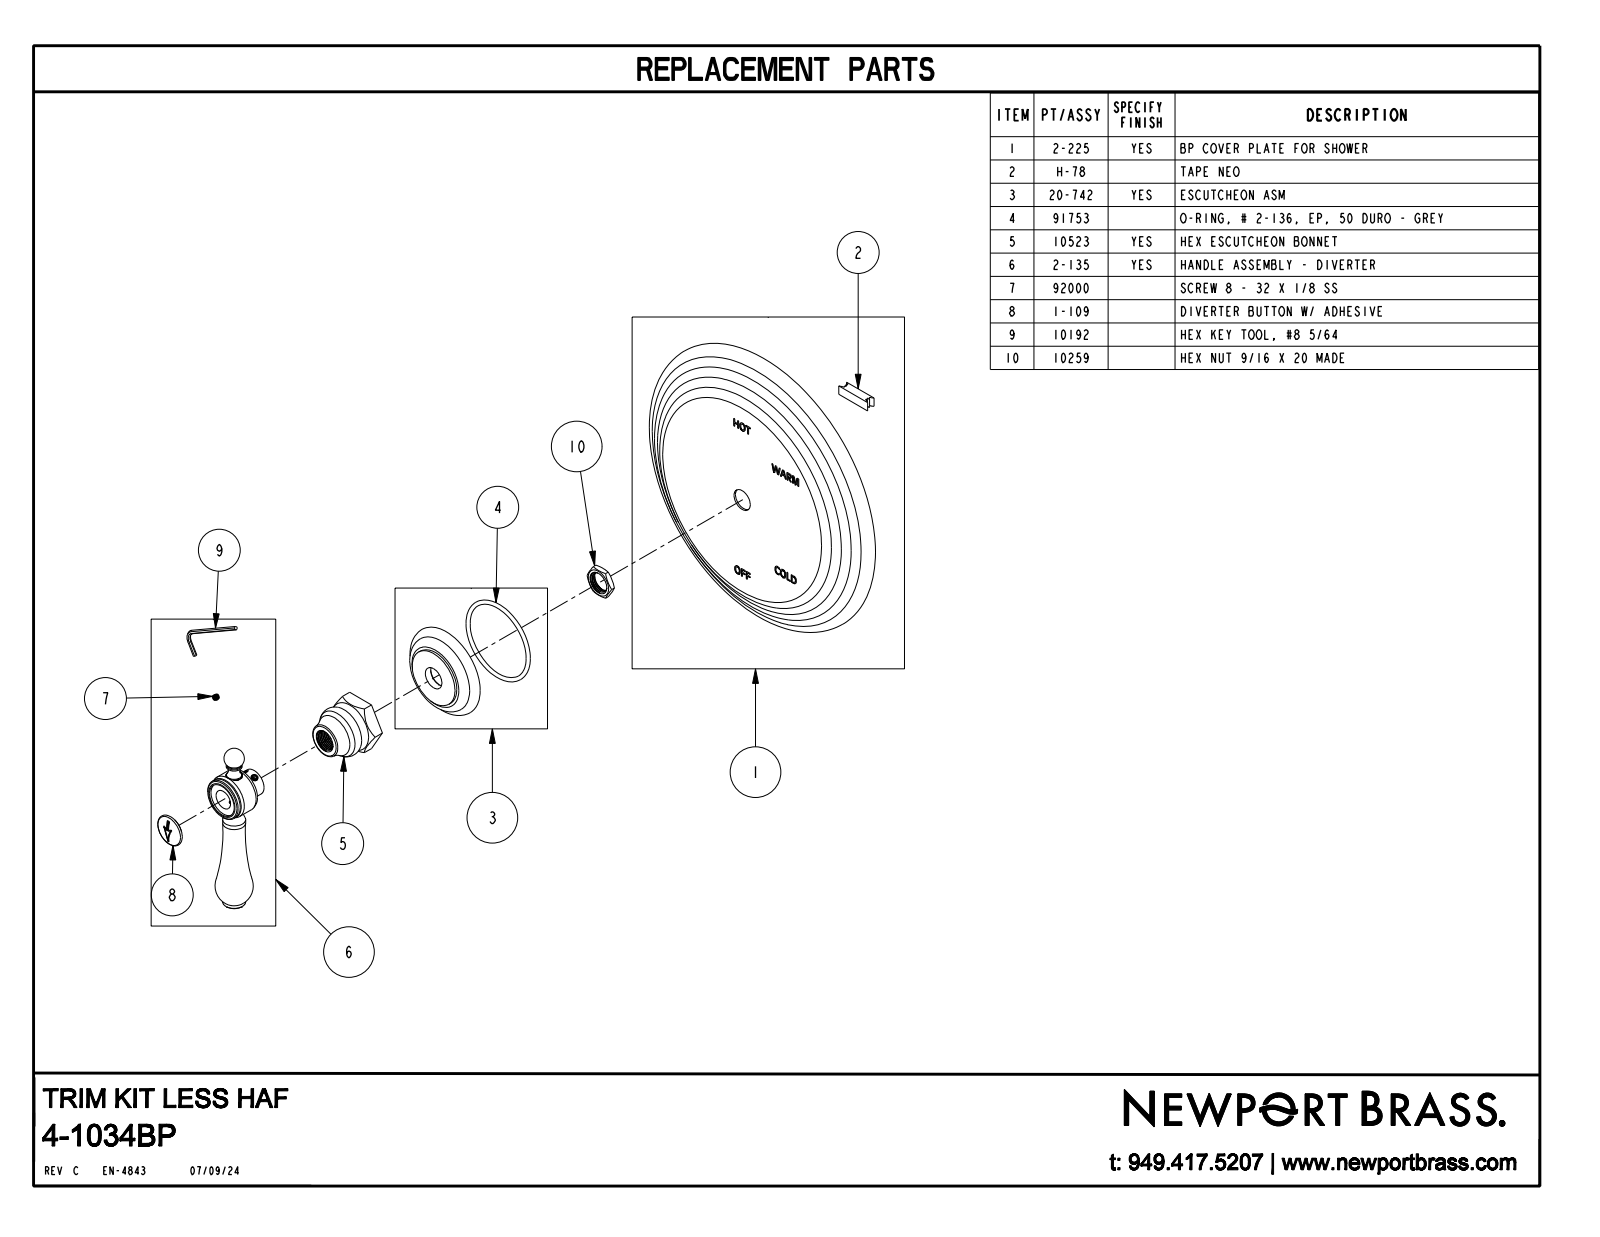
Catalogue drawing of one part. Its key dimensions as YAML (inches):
part_name: "4-1034BP"
step_written_by: "CREO PARAMETRIC BY PTC INC, 2018400 (CONFIG_CONTROL_DESIGN)"
units: inches
bodies: {solids: 1, faces: 345, planar: 166, cylindrical: 31, other: 148}
overall_size: [7.75, 7.75, 3.656]
volume: 32.47
surface_area: 119.5
round_holes:
  - {diameter: 0.41, count: 1}
  - {diameter: 0.855, count: 1}
round_bosses_or_shafts:
  - {diameter: 1.482, count: 1}
  - {diameter: 1.115, count: 1}
  - {diameter: 1.055, count: 1}
  - {diameter: 0.687, count: 1}
  - {diameter: 0.563, count: 1}
  - {diameter: 0.4, count: 1}
  - {diameter: 0.394, count: 1}
  - {diameter: 0.392, count: 1}
partial_cylinders:
  - {radius: 0.015, count: 2}
  - {radius: 1, count: 2}
  - {radius: 1.02, count: 2}
  - {radius: 0.02, count: 1}
face_to_face_distances: [0.754, 1.313, 2.441, 1.687, 1.129, 0.375, 1.312, 0.75, 0.379, 1.691]
